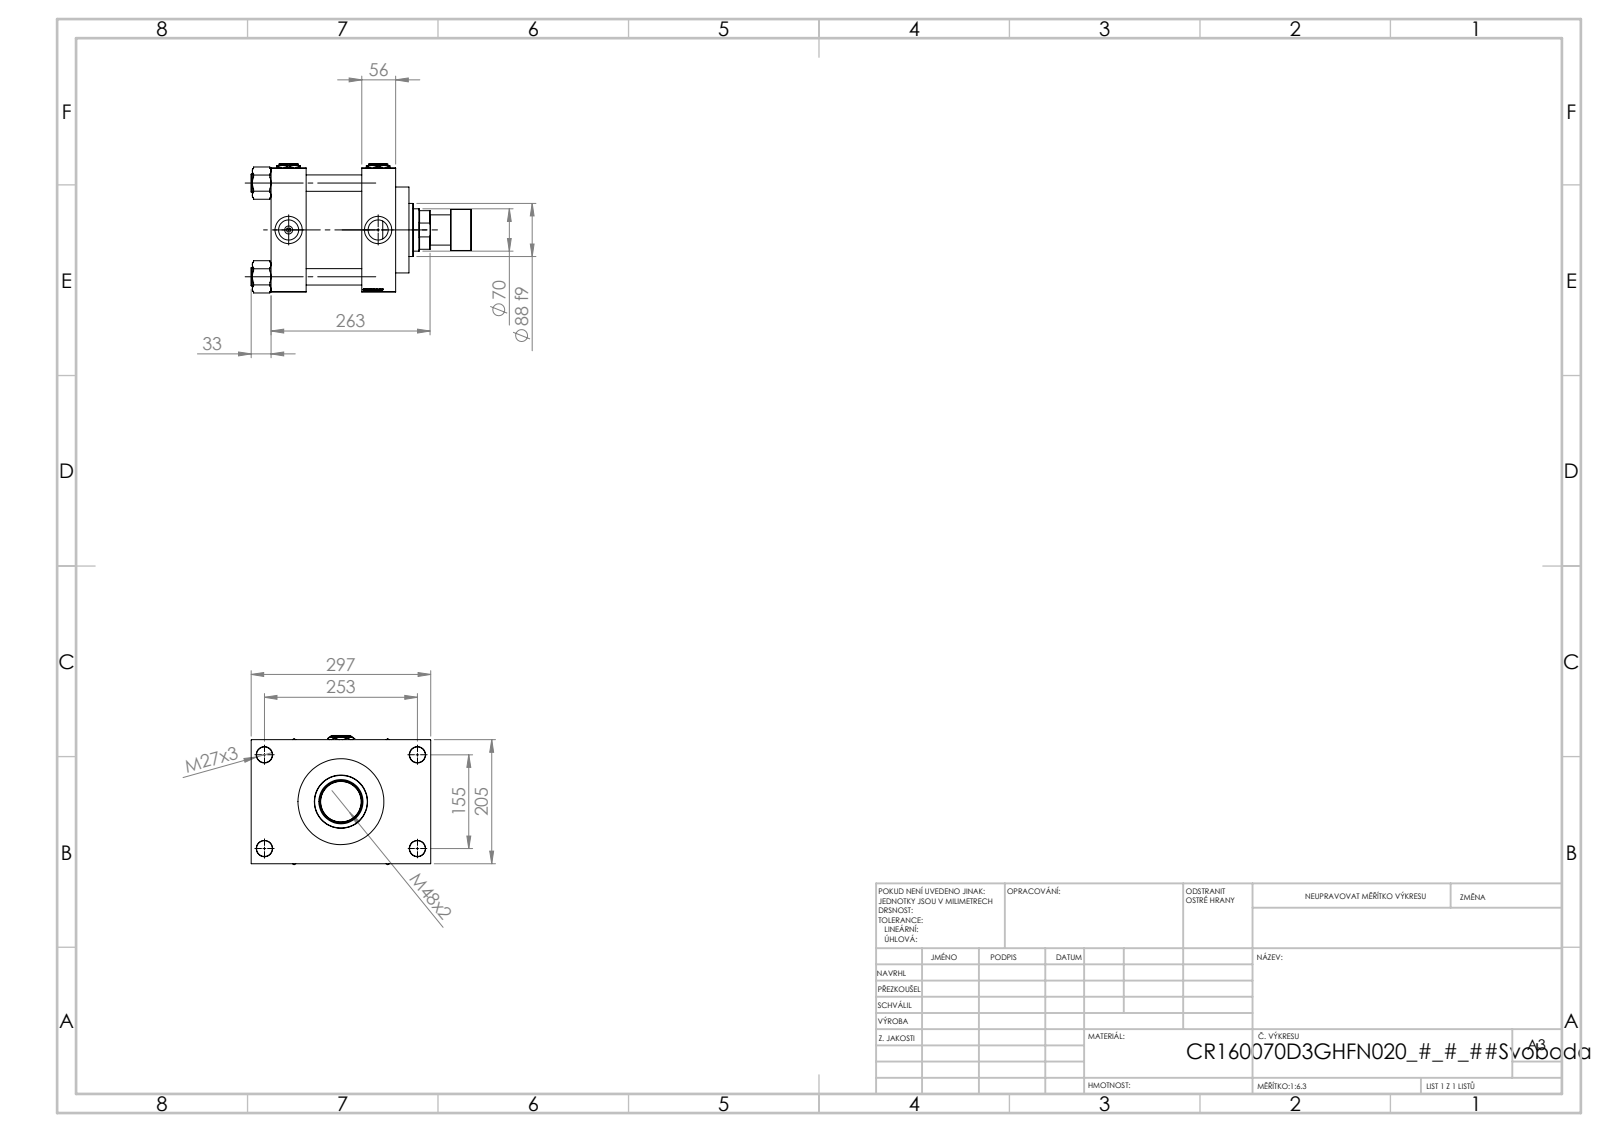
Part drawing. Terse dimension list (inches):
name: V215CR_D_TYCINKA; V215CR_VCP_D; V215_VC_A; V215CR_D_Body (+3 more)
written by: SolidWorks 2019 (CONFIG_CONTROL_DESIGN)
unit: in
bodies: 14 solids, 1263 faces (596 planar, 103 cylindrical, 564 other)
size: 14.331 × 11.693 × 8.408
volume: 489 in³; area: 1 180 in²
holes: 4× ⌀1.024, 4× ⌀1.063, 4× ⌀1.309, 4× ⌀1.772, 3× ⌀0.276, 1× ⌀1.831, 1× ⌀2.756, 1× ⌀2.874, 1× ⌀4.724, 1× ⌀5.591, 1× ⌀6.299
bosses: 4× ⌀1.181, 1× ⌀6.535, 1× ⌀3.465, 1× ⌀2.677, 1× ⌀1.969, 1× ⌀1.929
face distances: 2.283, 5.906, 3.622, 5.827, 8.11, 2.205, 8.071, 1.811, 9.882, 2.835
hole spacings: 1.931, 4.312, 5.841, 6.098, 6.399, 8.03, 10.084, 5.827
